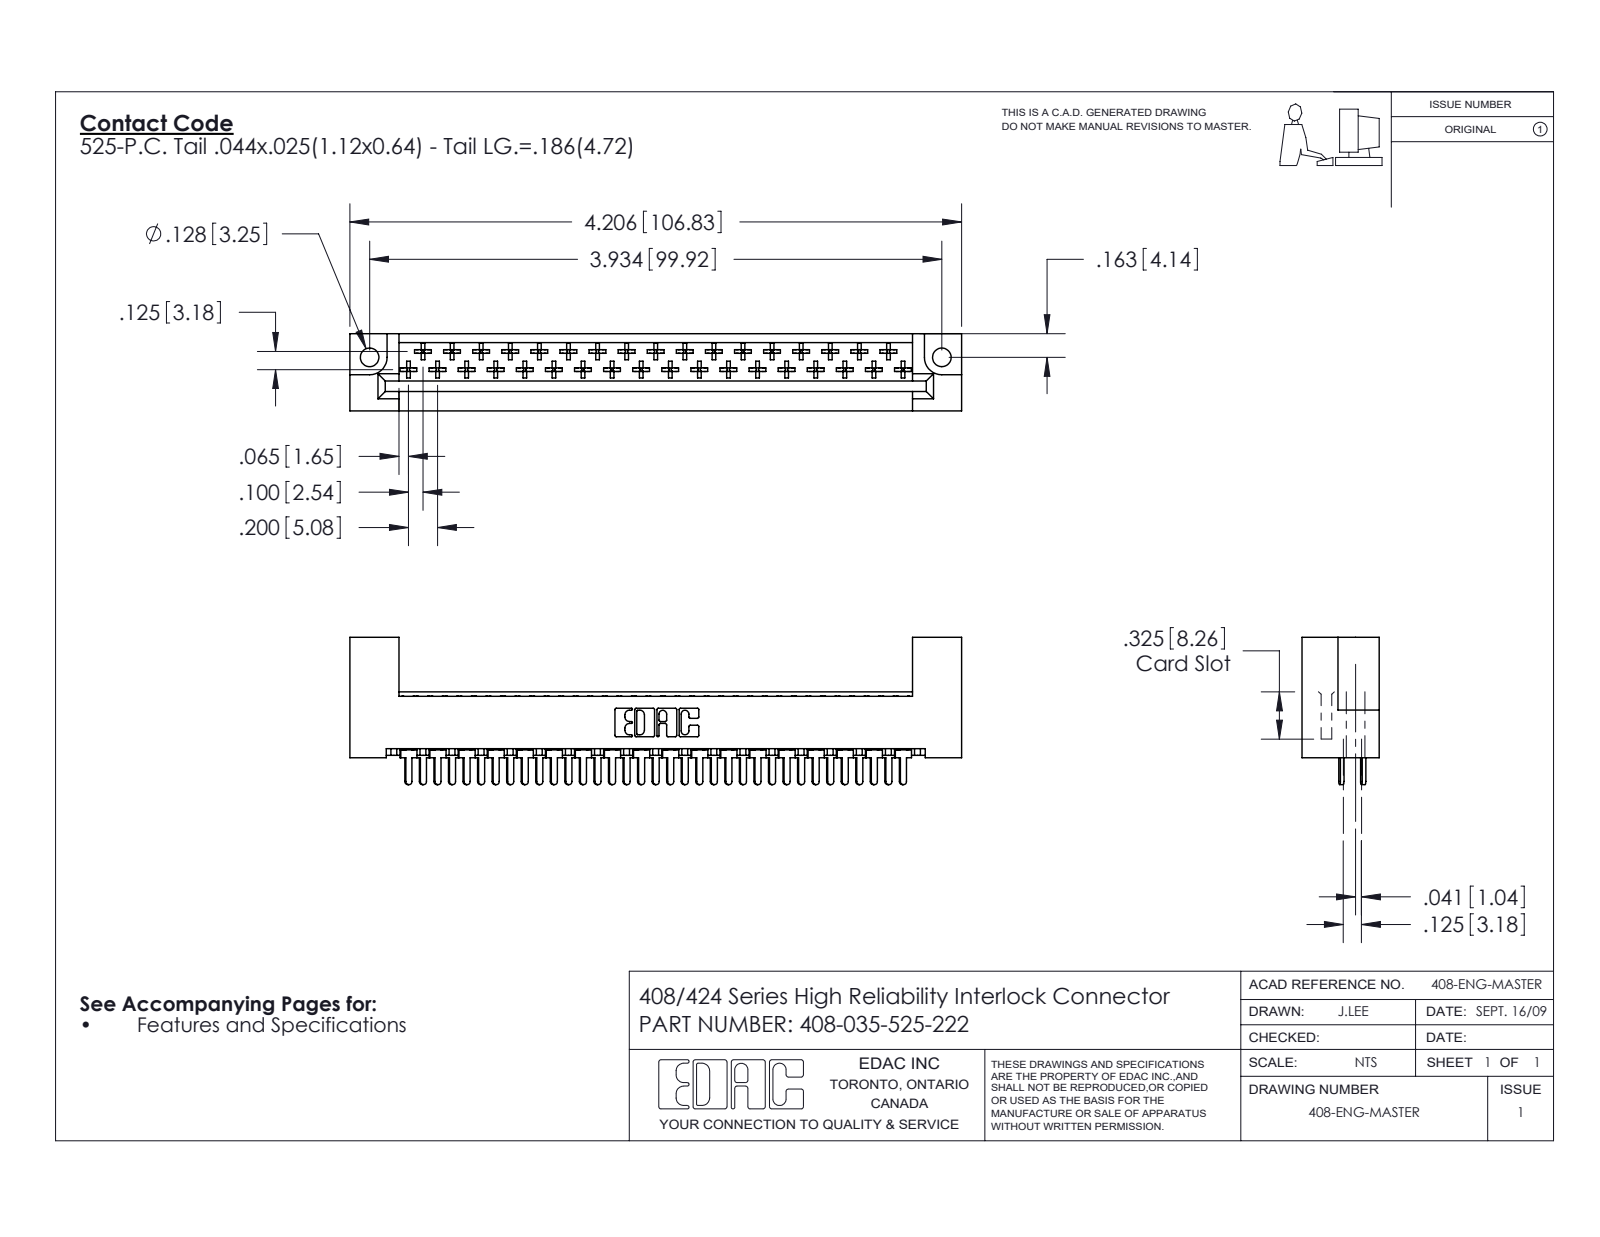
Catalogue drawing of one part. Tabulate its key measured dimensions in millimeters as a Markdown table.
| quantity | value |
| --- | --- |
| part name | 408-290-001_408-290-125 - Bottom; 408-035-525-222; 408 Part_035 - 2; 408-290-001_408-290-125 - Top |
| STEP written by | SolidWorks 2016 (CONFIG_CONTROL_DESIGN) |
| units | millimeters |
| bodies | 36 solids, 2064 faces (1559 planar, 365 cylindrical, 140 other) |
| overall size | 106.8 × 25.7 × 13.5 |
| volume | 13 400 mm³ |
| surface area | 15 520 mm² |
| round holes (diameter × count) | 3.3 × 2 |
| partial cylindrical surfaces (radius × count) | 0.3 × 210, 0.5 × 37, 0.6 × 35, 0.3 × 22, 0.2 × 6, 0.8 × 6, 0.7 × 3, 3 × 2 |
| main face-to-face distances | 13.5, 3.2, 2.5, 0.6, 0.6, 9.2, 6, 6.6, 10.1, 5.5 |
| hole center spacings | 99.9 |
